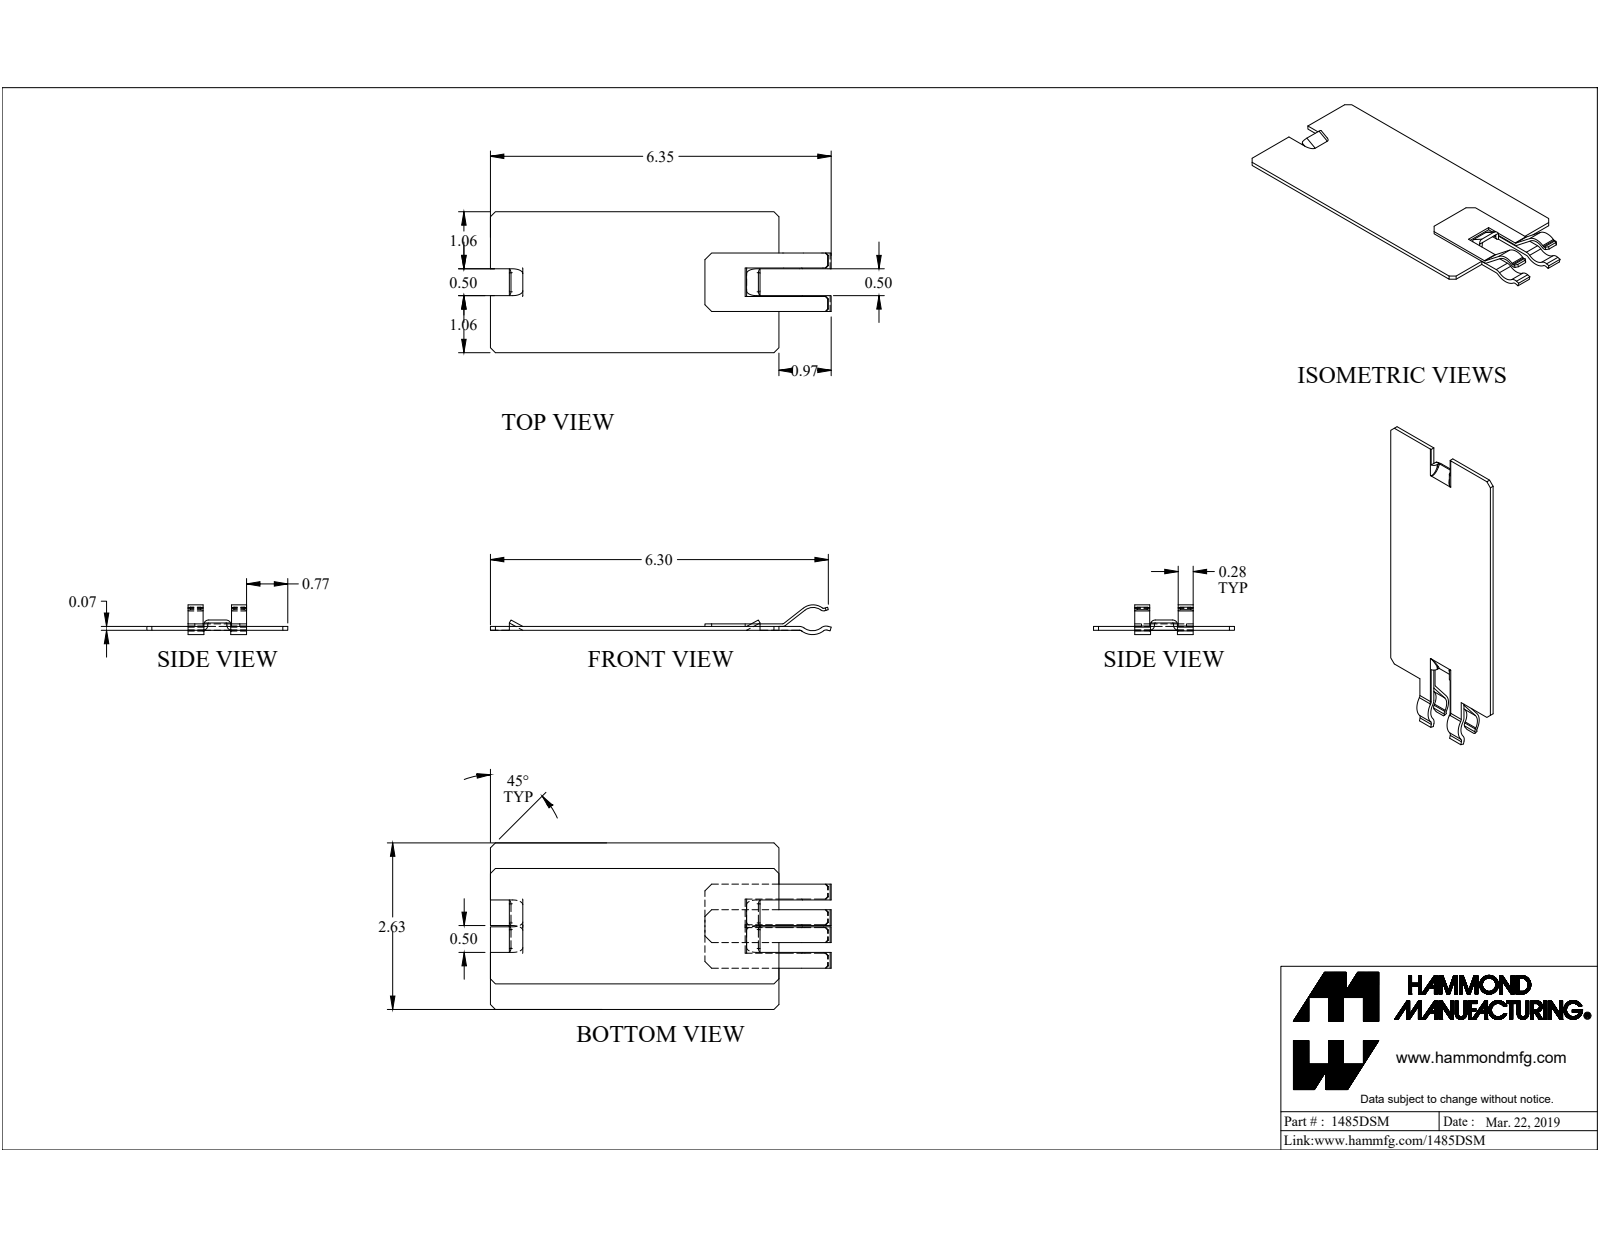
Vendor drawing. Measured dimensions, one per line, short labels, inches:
name: 1485DSM
written by: SolidWorks 2019 (CONFIG_CONTROL_DESIGN)
unit: in
bodies: 4 solids, 125 faces (83 planar, 36 cylindrical, 6 other)
size: 6.348 × 2.625 × 0.599
volume: 1.608 in³; area: 43.81 in²
rounds: 6× R0.09, 4× R0.015, 3× R0.072, 2× R0.144, 1× R0.024, 1× R0.03, 1× R0.078, 1× R0.245
face distances: 0.072, 0.125, 0.197, 0.048, 0.245, 0.12, 0.75, 4.543, 2.625, 0.768
